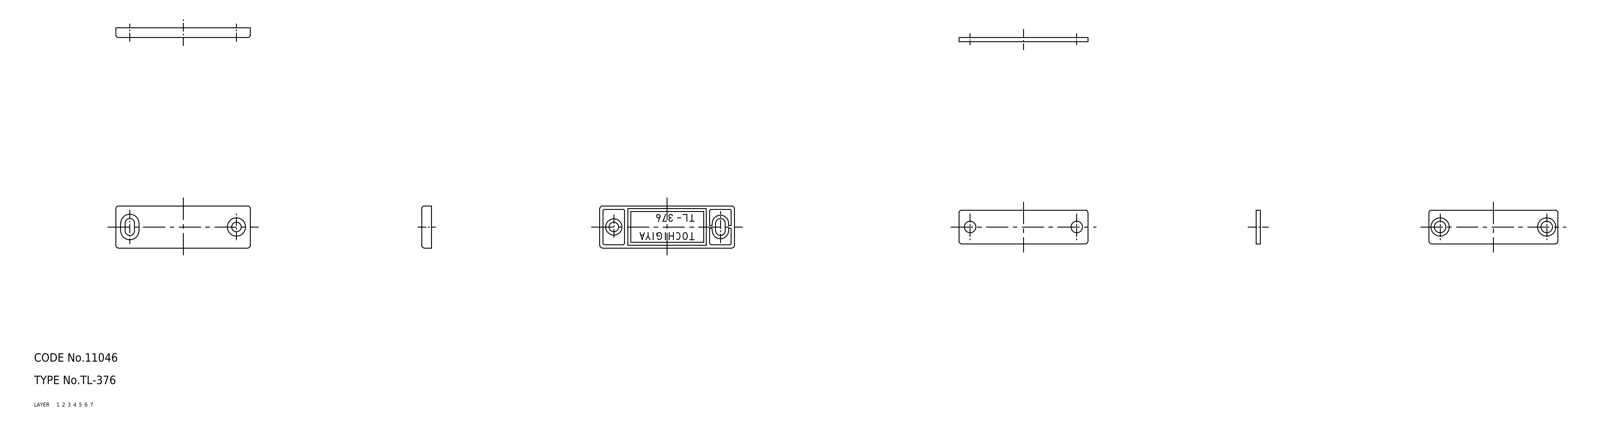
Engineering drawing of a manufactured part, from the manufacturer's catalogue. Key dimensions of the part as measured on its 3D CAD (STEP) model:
Part name (STEP PRODUCT): 67113009; 67113022
STEP written by: CADfix (AUTOMOTIVE_DESIGN)
Units: millimetres
Bodies: 2 solids, 93 faces (0 planar, 0 cylindrical, 93 other)
Overall size (bounding box): 48 × 30 × 15
Volume: 2 813 mm³ · Surface area: 3 506 mm²
